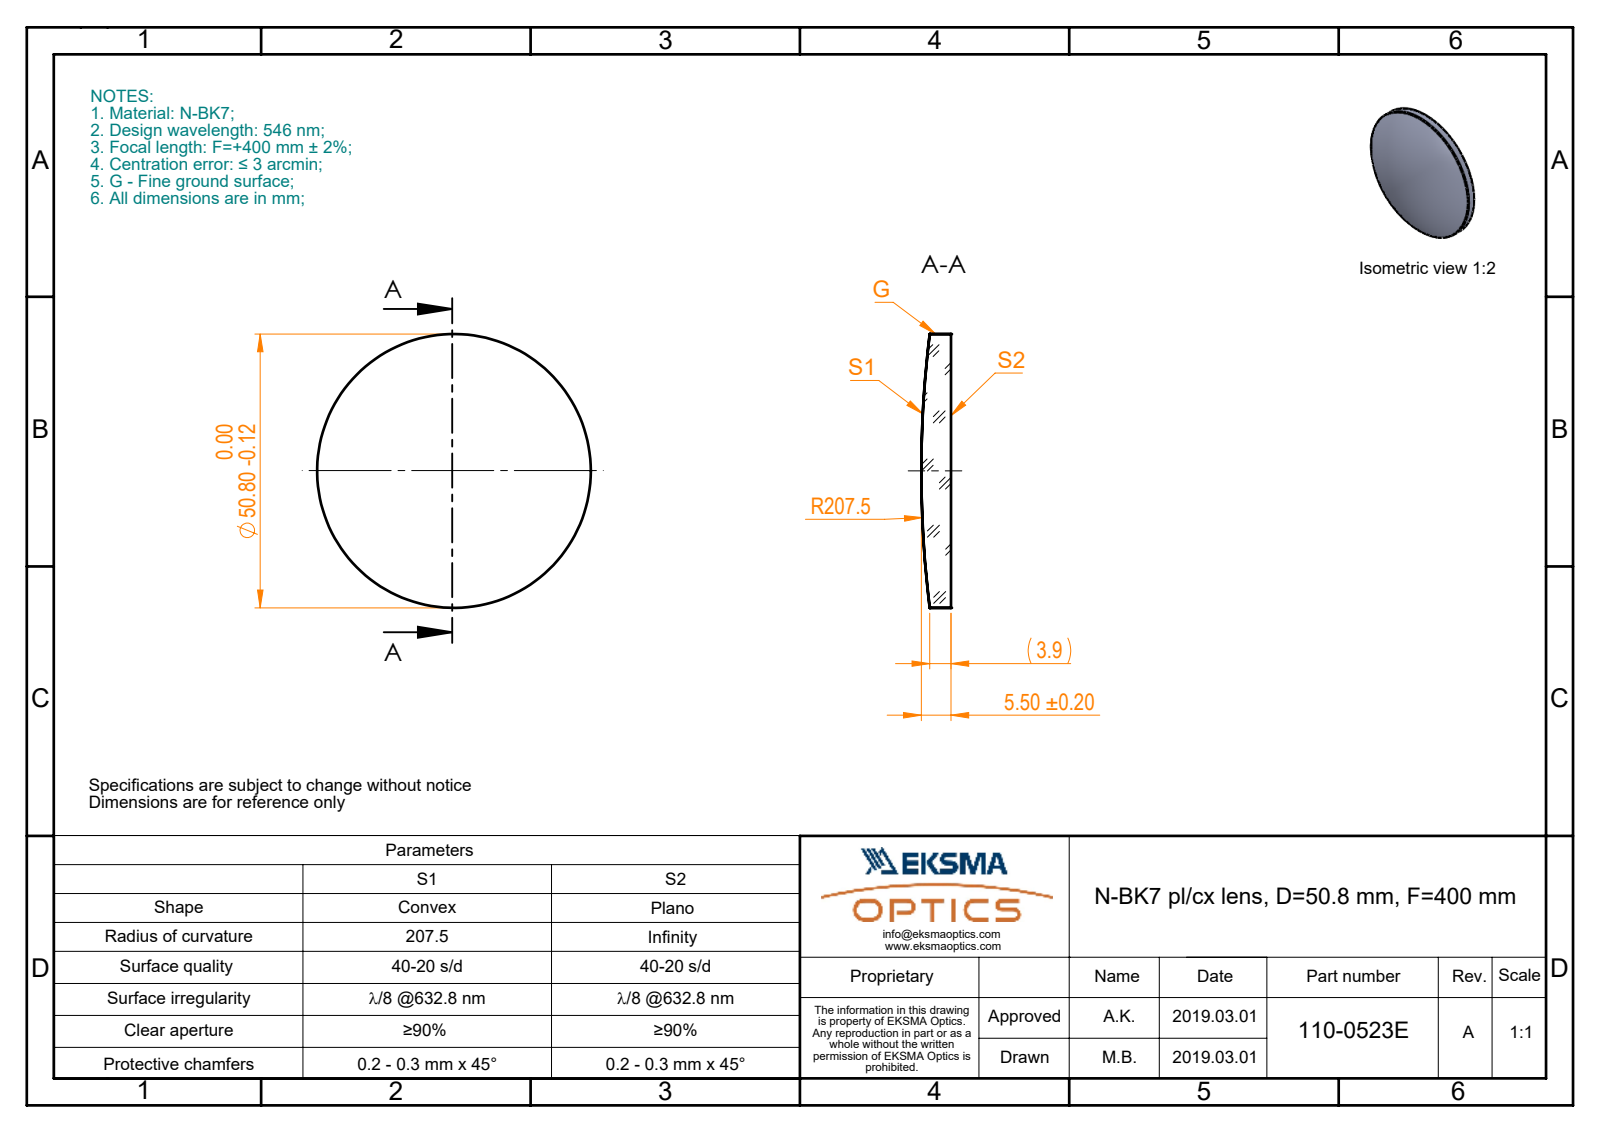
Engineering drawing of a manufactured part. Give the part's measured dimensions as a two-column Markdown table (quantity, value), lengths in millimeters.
| quantity | value |
| --- | --- |
| part name | 110-0523E BK7 pl-cx 50.8 F400 |
| STEP written by | SolidWorks 2017 (CONFIG_CONTROL_DESIGN) |
| units | millimeters |
| bodies | 1 solid, 5 faces (1 planar, 2 cylindrical, 2 other) |
| overall size | 50.8 × 50.8 × 5.5 |
| volume | 9 568 mm³ |
| surface area | 4 690 mm² |
| round bosses / shafts (diameter × count) | 50.8 × 1 |
